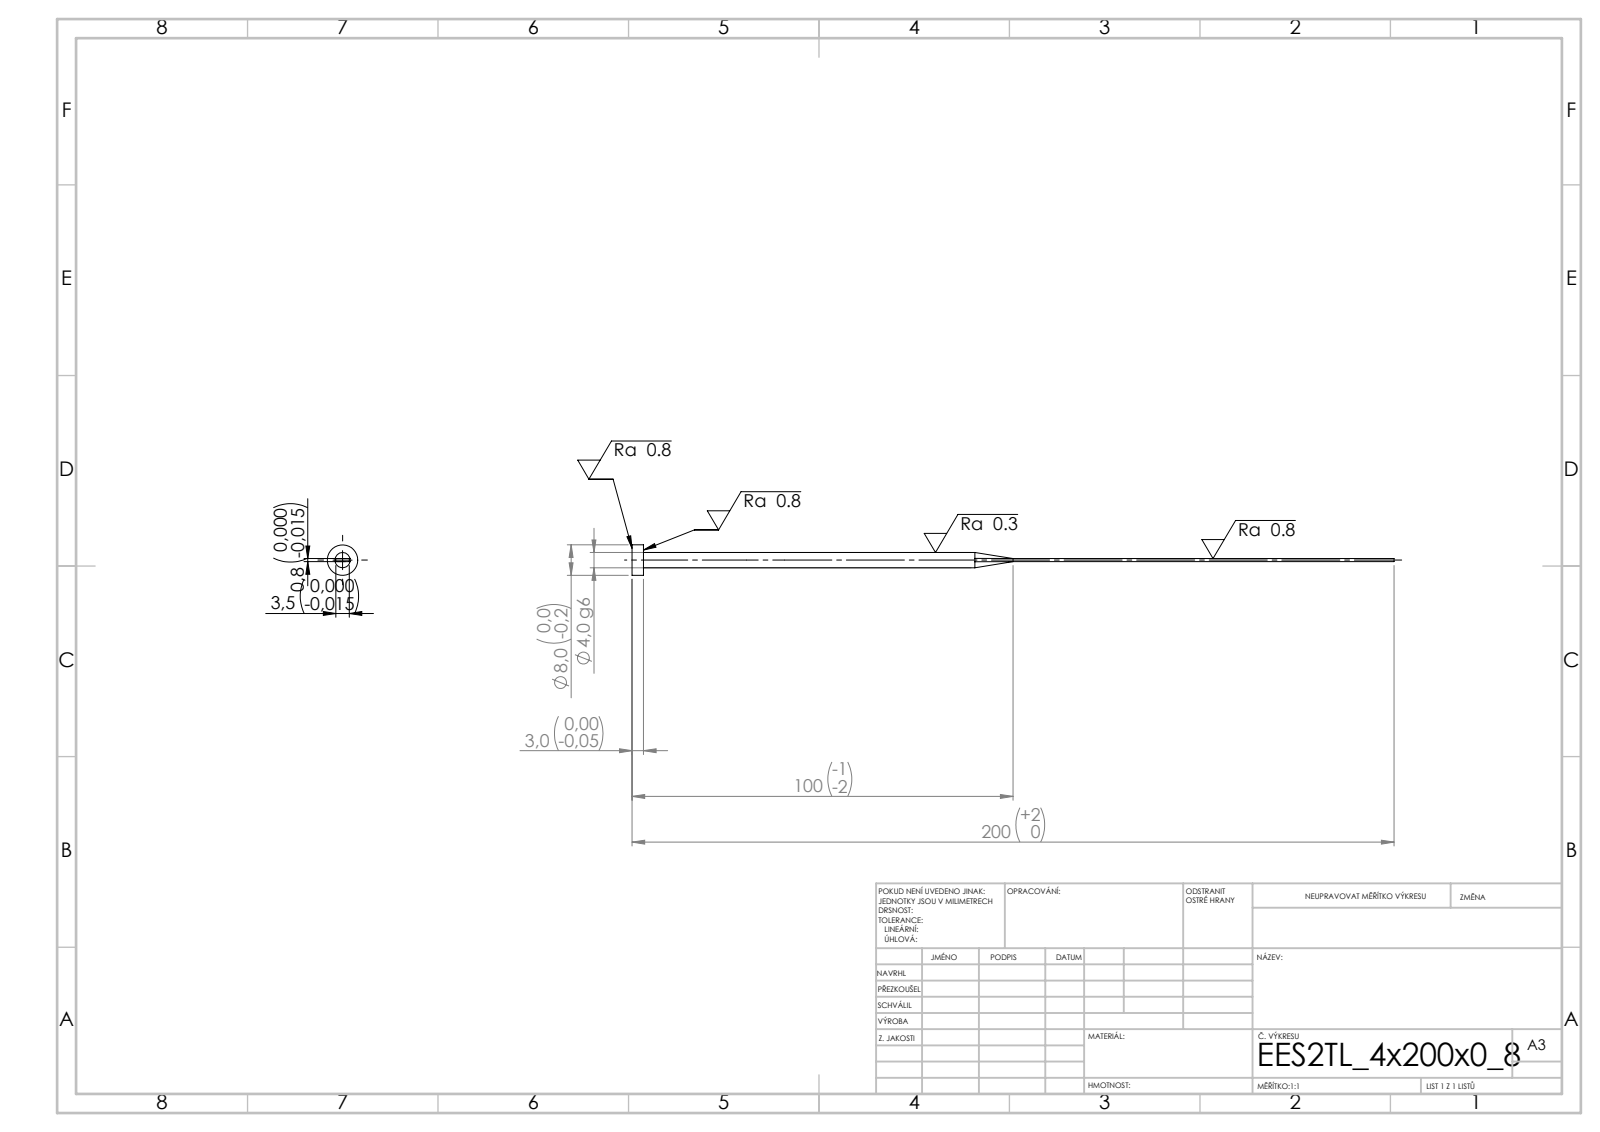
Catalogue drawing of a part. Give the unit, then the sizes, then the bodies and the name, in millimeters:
Units: millimetres
Overall size (bounding box): 200 × 8 × 8
Round bosses / shafts (diameter × count): ⌀8 ×1, ⌀4 ×1
Main face-to-face distances: 0.8, 3.5, 3, 200, 197
Volume: 1 597 mm³ · Surface area: 2 221 mm²
Bodies: 1 solid, 15 faces (7 planar, 4 cylindrical, 4 other)
STEP written by: SolidWorks 2019 (CONFIG_CONTROL_DESIGN)
